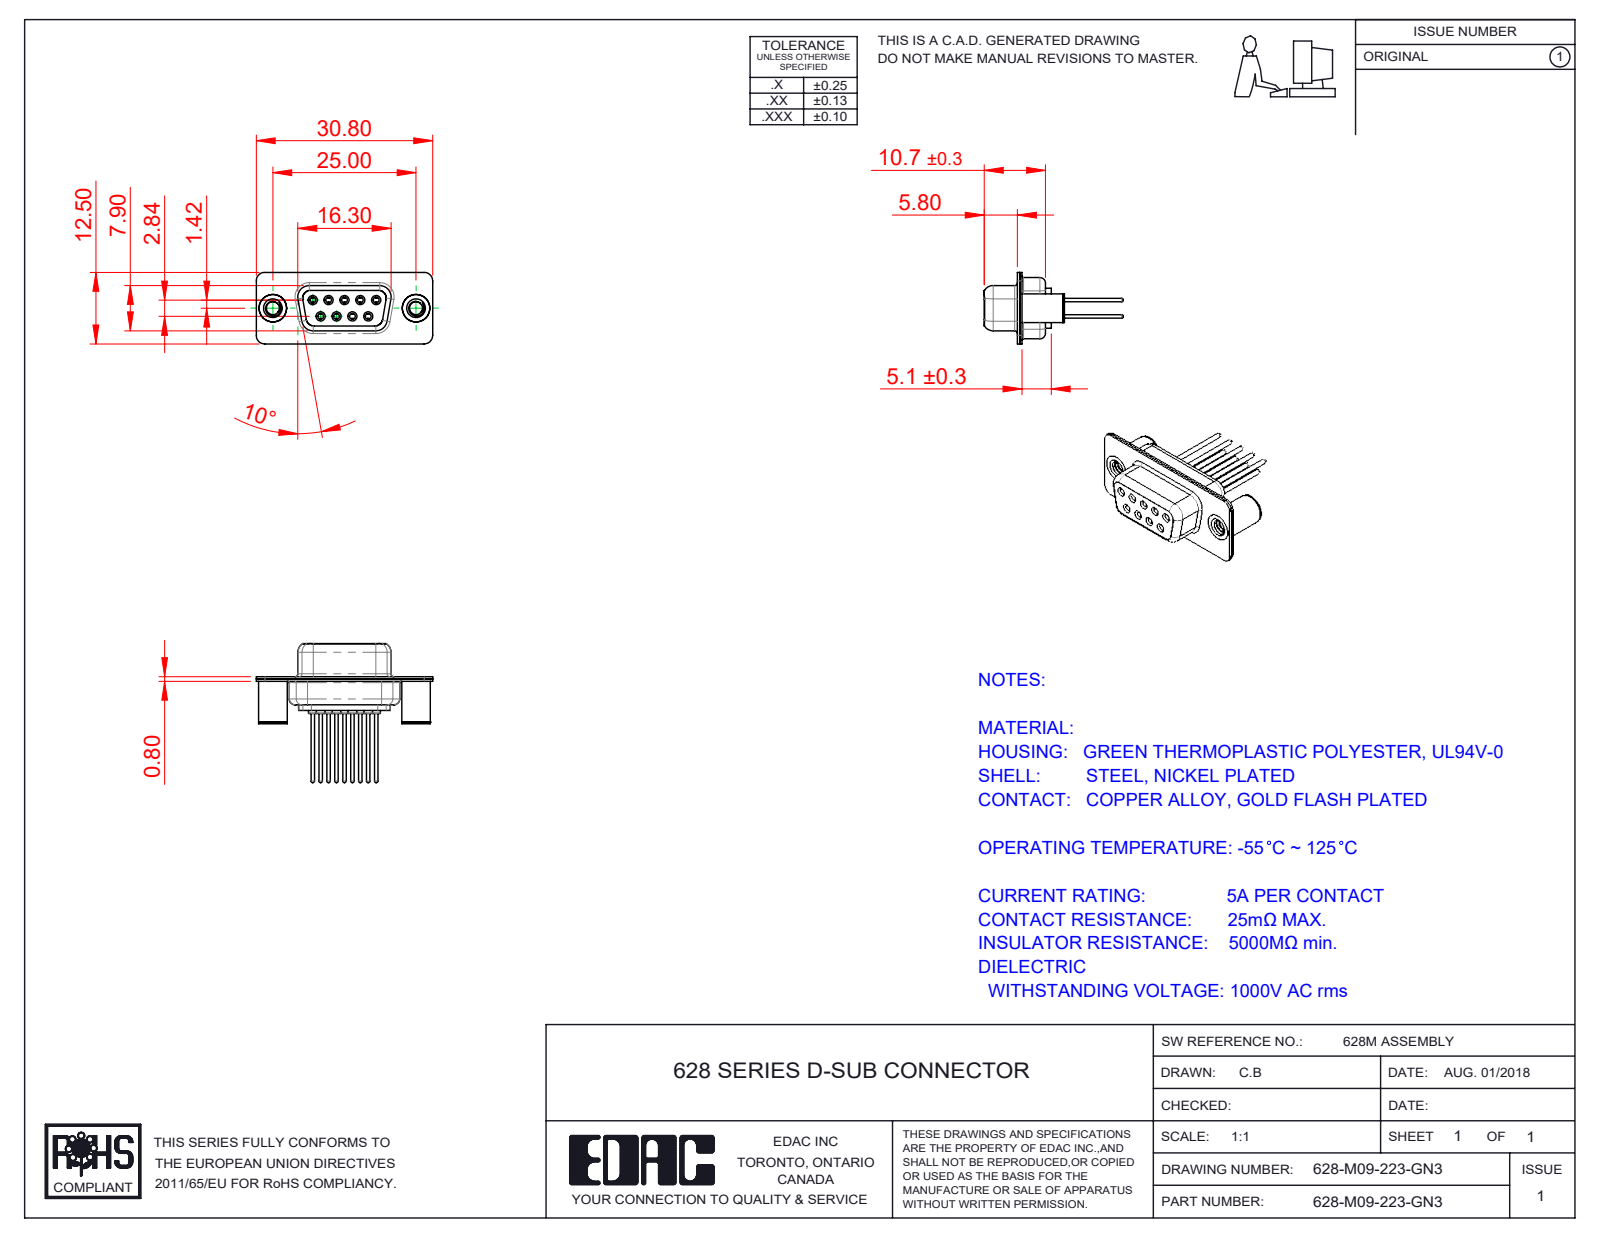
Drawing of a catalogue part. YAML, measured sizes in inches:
part_name: "628M 4-40 Threaded Board Spacer; 628M Shell Front_09 Contacts; 628M Contact Row 1_23; 628M Shell Rear_09 Contacts (+3 more)"
step_written_by: "SolidWorks 2020 (CONFIG_CONTROL_DESIGN)"
units: inches
bodies: {solids: 14, faces: 808, planar: 202, cylindrical: 332, other: 274}
overall_size: [1.213, 0.956, 0.492]
volume: 0.112
surface_area: 7.431
round_holes:
  - {diameter: 0.039, count: 9}
  - {diameter: 0.043, count: 9}
  - {diameter: 0.067, count: 9}
  - {diameter: 0.071, count: 9}
  - {diameter: 0.079, count: 9}
  - {diameter: 0.089, count: 2}
  - {diameter: 0.128, count: 2}
  - {diameter: 0.157, count: 2}
  - {diameter: 0.189, count: 2}
round_bosses_or_shafts:
  - {diameter: 0.087, count: 9}
  - {diameter: 0.063, count: 9}
  - {diameter: 0.059, count: 9}
  - {diameter: 0.024, count: 9}
  - {diameter: 0.197, count: 2}
  - {diameter: 0.193, count: 2}
partial_cylinders:
  - {radius: 0.059, count: 16}
  - {radius: 0.079, count: 12}
  - {radius: 0.053, count: 8}
  - {radius: 0.063, count: 8}
  - {radius: 0.01, count: 4}
  - {radius: 0.02, count: 4}
  - {radius: 0.024, count: 4}
  - {radius: 0.026, count: 4}
face_to_face_distances: [0.016, 0.055, 0.018, 0.333, 0.031, 0.071, 0.35, 0.039, 0.244, 0.278]
hole_center_spacings: [0.124, 0.109, 0.218, 0.198, 0.198, 0.327, 0.28, 0.294]
